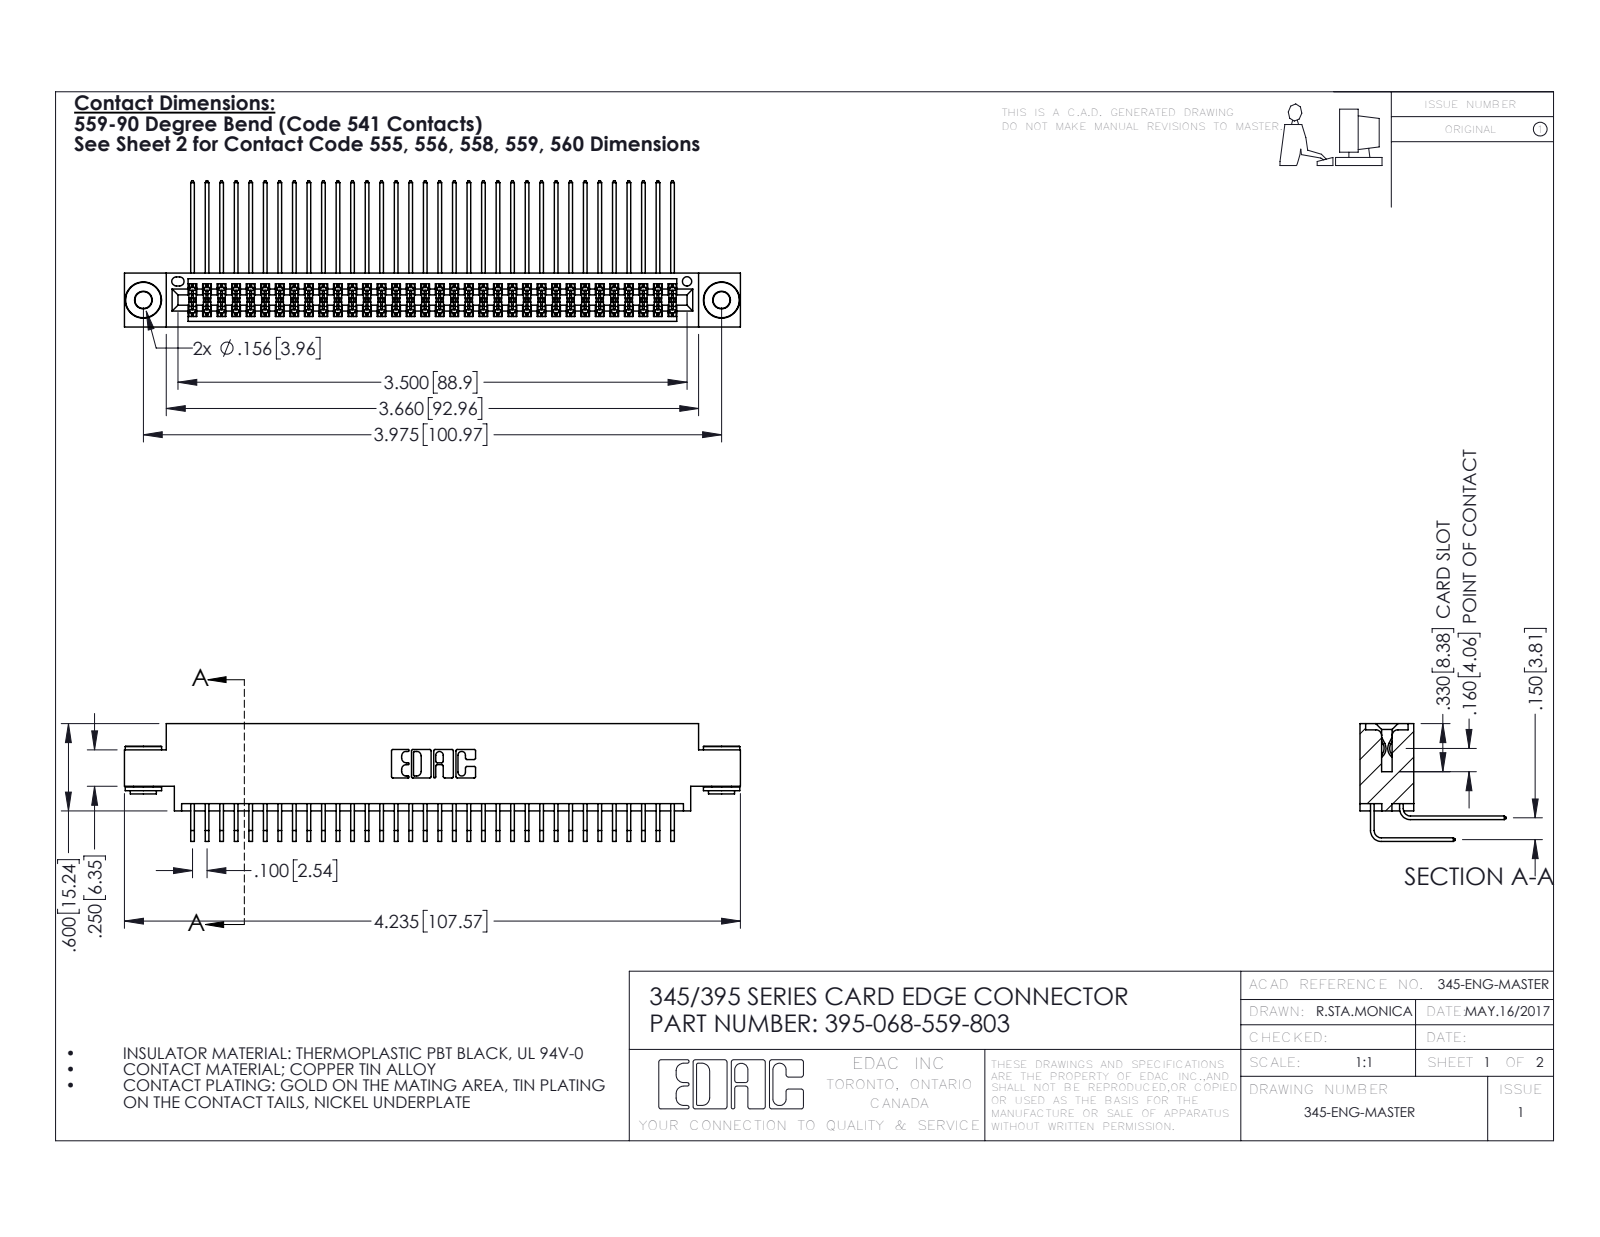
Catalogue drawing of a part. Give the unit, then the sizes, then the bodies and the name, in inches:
Units: inches
Overall size (bounding box): 4.235 × 1.005 × 0.809
Round holes (diameter × count): ⌀0.116 ×2, ⌀0.156 ×2, ⌀0.064 ×1
Round bosses / shafts (diameter × count): ⌀0.25 ×2, ⌀0.18 ×2, ⌀0.136 ×2
Partial cylindrical surfaces — rounded edges, fillets, slot ends (radius × count): R0.006 ×103, R0.01 ×22, R0.007 ×6, R0.031 ×6, R0.026 ×3, R0.014 ×2, R0.019 ×2, R0.022 ×2
Main face-to-face distances: 0.072, 0.298, 0.37, 0.2, 0.098, 0.272, 0.025, 0.175, 0.15, 0.225
Hole centre spacings: 0.27, 3.74, 3.975
Volume: 0.651 in³ · Surface area: 27.61 in²
Bodies: 71 solids, 3704 faces (2474 planar, 1222 cylindrical, 8 other)
Part name (STEP PRODUCT): 345-292-001_558 559 Tail - 1; 345-292-001_559 Tail - 2; 395-068-559-803; 345-250-002_345-250-002-102 (+1 more)
STEP written by: SolidWorks 2016 (CONFIG_CONTROL_DESIGN)
